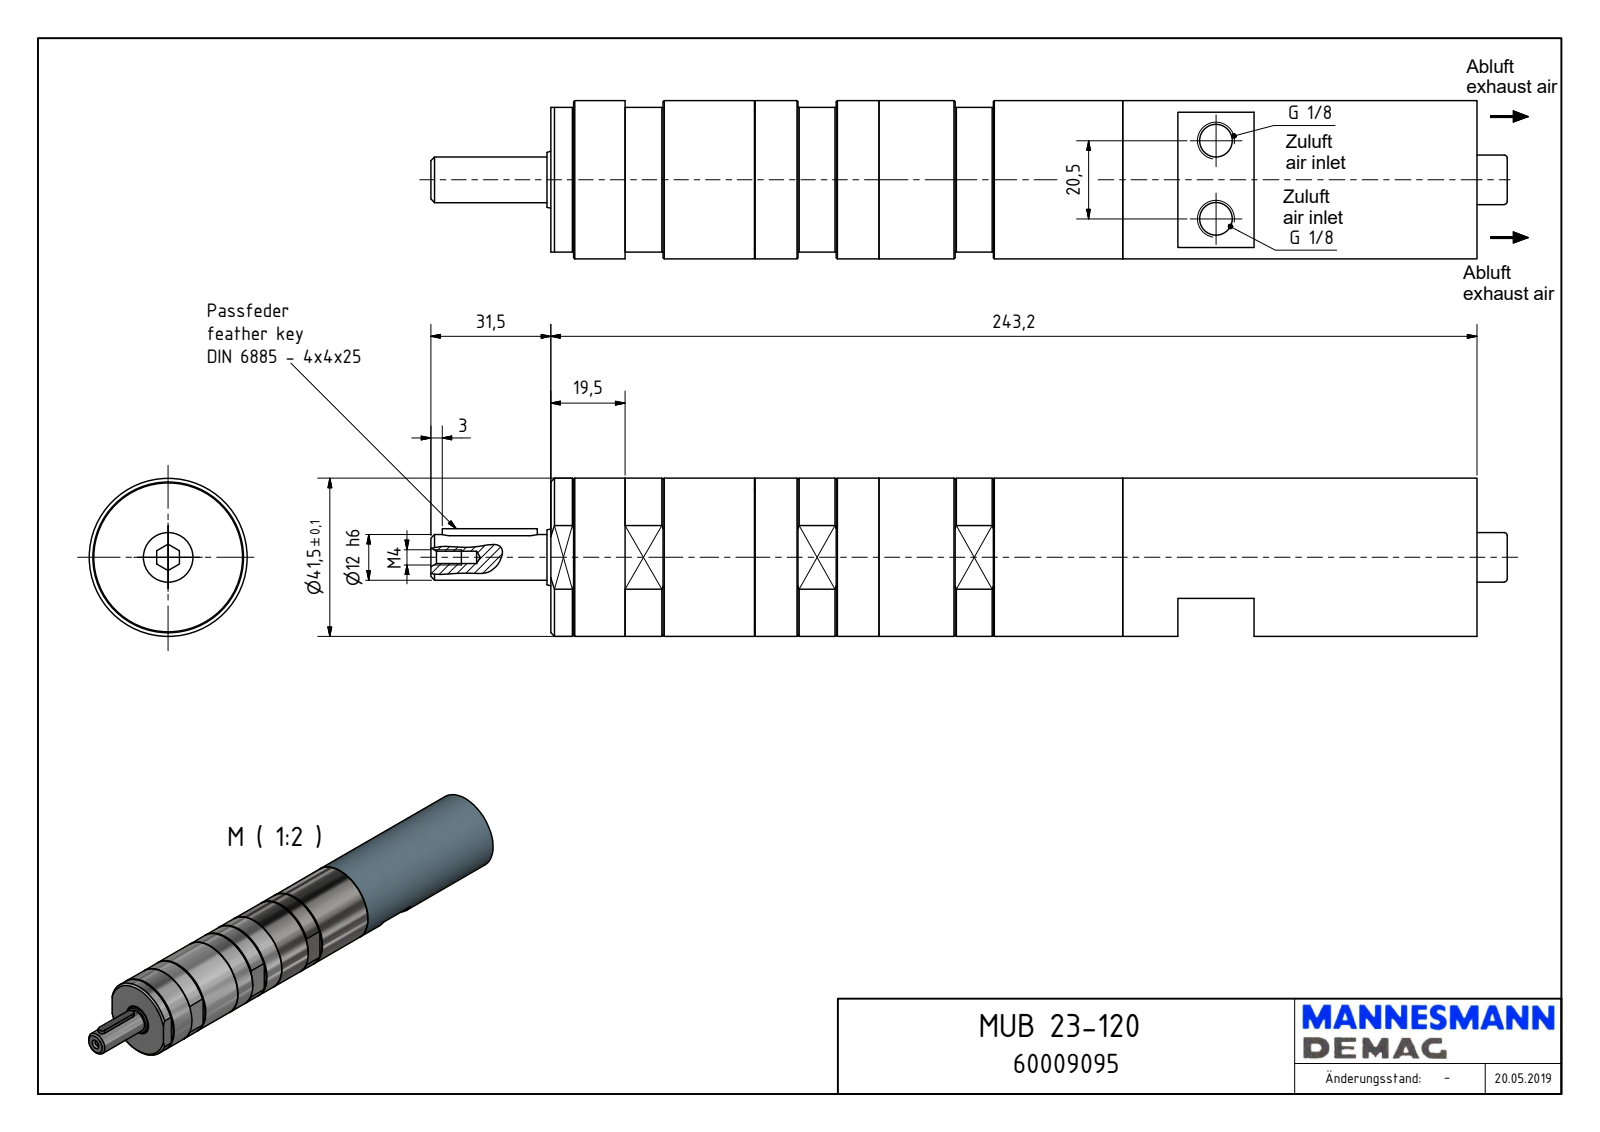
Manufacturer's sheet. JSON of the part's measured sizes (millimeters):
{"part_name": "MUB 23-120_60009095", "step_written_by": "Autodesk Inventor 2018 (AUTOMOTIVE_DESIGN)", "units": "millimeters", "bodies": {"solids": 1, "faces": 156, "planar": 69, "cylindrical": 57, "other": 30}, "overall_size": [282.7, 41.5, 41.5], "volume_mm3": 324624, "surface_area_mm2": 40888, "round_holes": [[2, 2], [8.57, 2], [3.24, 1], [8.5, 1], [13, 1], [16, 1], [39.5, 1]], "round_bosses_or_shafts": [[41.5, 1], [39.2, 1], [39, 1], [36, 1], [14.95, 1], [12, 1], [8, 1]], "partial_cylinders_radius": [[2, 4], [1.6, 2], [2.5, 2], [4.5, 1], [8.1, 1], [12.18, 1]], "face_to_face_distances": [243.2, 38, 53.5, 189.7, 53.7, 189.5, 58.5, 78.5, 184.7, 131.2], "hole_center_spacings": [12.94, 20.5, 25]}
